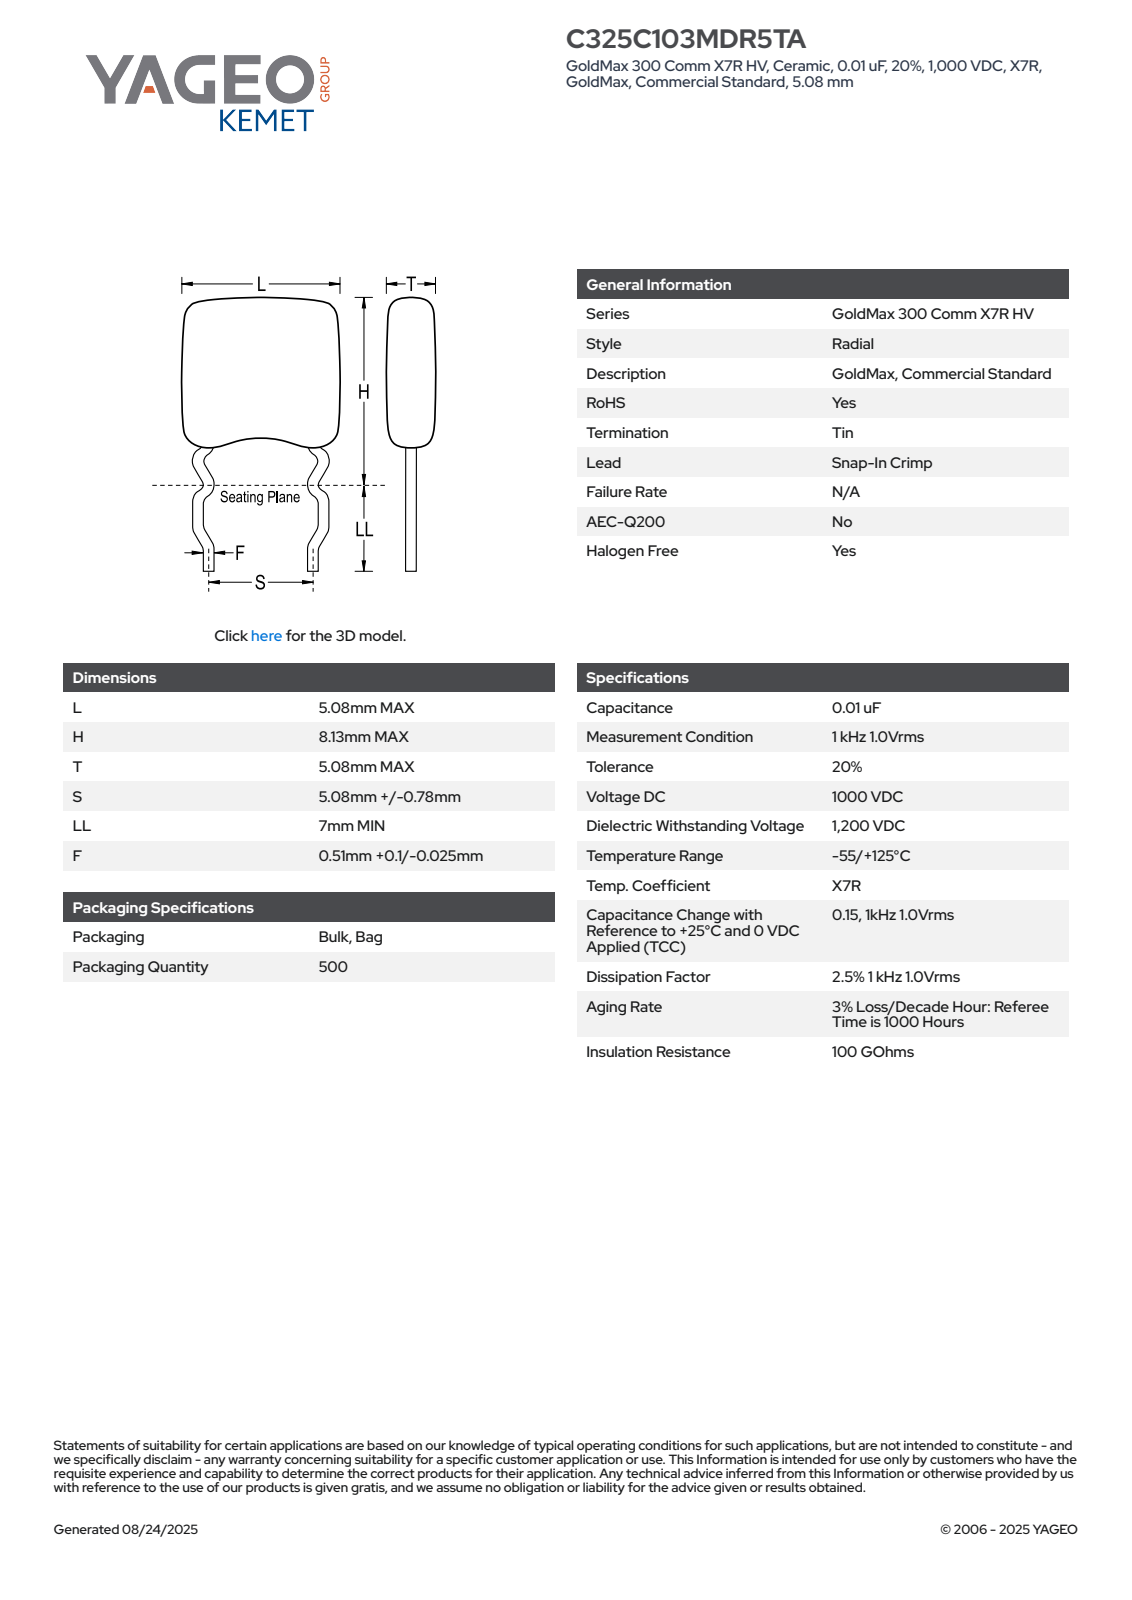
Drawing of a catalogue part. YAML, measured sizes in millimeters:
part_name: "CCR_SICR_5.08X8.13_L5.08H8.13T5.08S5.08LL7F0.51"
step_written_by: "SolidWorks 2014 (AUTOMOTIVE_DESIGN)"
units: millimeters
bodies: {solids: 4, faces: 157, planar: 68, cylindrical: 46, other: 43}
overall_size: [15.49, 7.15, 5.08]
volume: 117
surface_area: 165
round_bosses_or_shafts:
  - {diameter: 0.51, count: 18}
partial_cylinders:
  - {radius: 1, count: 10}
face_to_face_distances: [5.08, 4.81, 10.68, 15.49, 2.13, 2.68, 13.36, 12.81, 0.55, 2.23]
